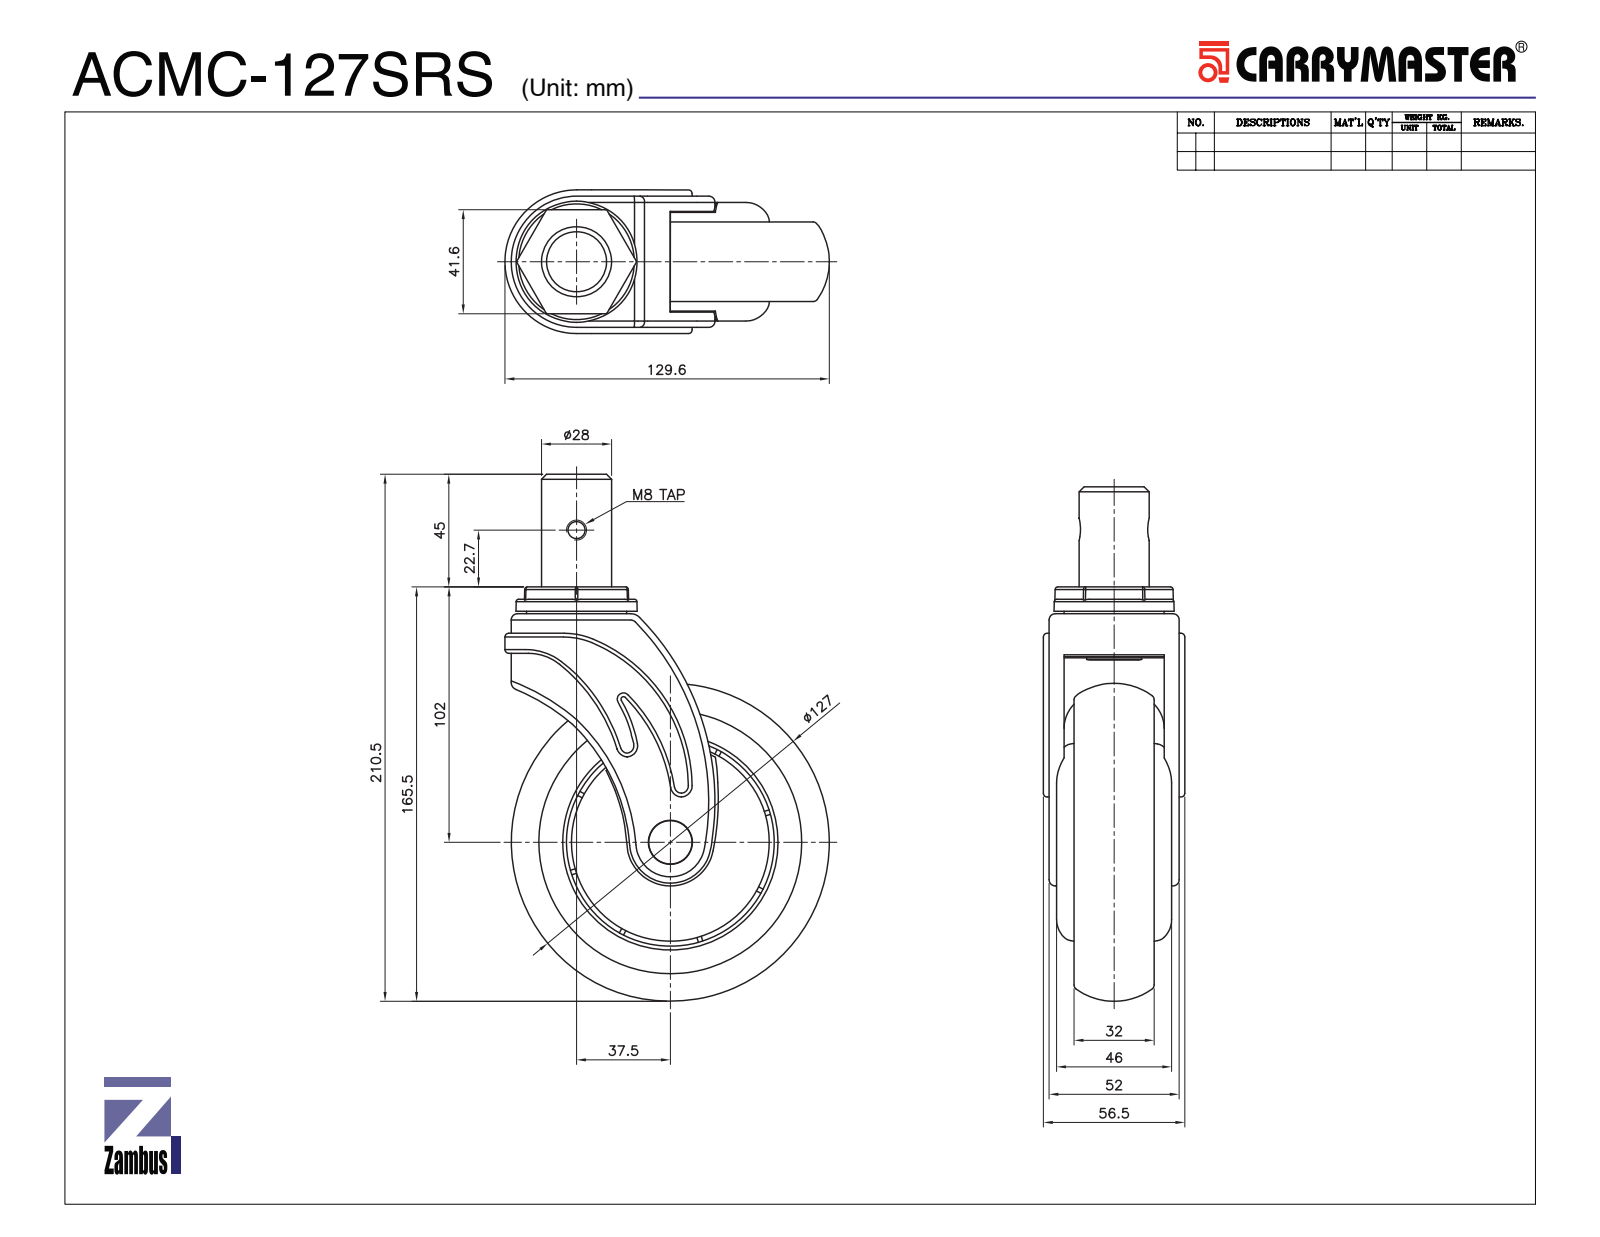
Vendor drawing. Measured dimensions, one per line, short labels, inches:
name: ACMC-127 WHEEL; ACMC-127 SRS TOP PLATE; ACMC-127 TOP PLATE COVER; ACMC-127SRS (+1 more)
written by: SolidWorks 2019 (CONFIG_CONTROL_DESIGN)
unit: in
bodies: 4 solids, 301 faces (68 planar, 142 cylindrical, 91 other)
size: 8.287 × 5.094 × 2.248
volume: 34.71 in³; area: 132.3 in²
holes: 1× ⌀0.268, 1× ⌀0.315, 1× ⌀0.681, 1× ⌀1.457, 1× ⌀3.268, 1× ⌀4.134
bosses: 1× ⌀4.134, 1× ⌀3.11, 1× ⌀3.094, 1× ⌀1.575, 1× ⌀1.102, 1× ⌀0.984, 1× ⌀0.866, 1× ⌀0.669
rounds: 13× R0.039, 4× R0.177, 2× R0.098, 1× R0.197, 1× R0.642, 1× R0.661, 1× R0.787, 1× R0.797
face distances: 0.167, 1.427, 1.26, 0.236, 0.404, 1.663, 1.831, 1.594, 0.157, 0.246
hole spacings: 5.127
